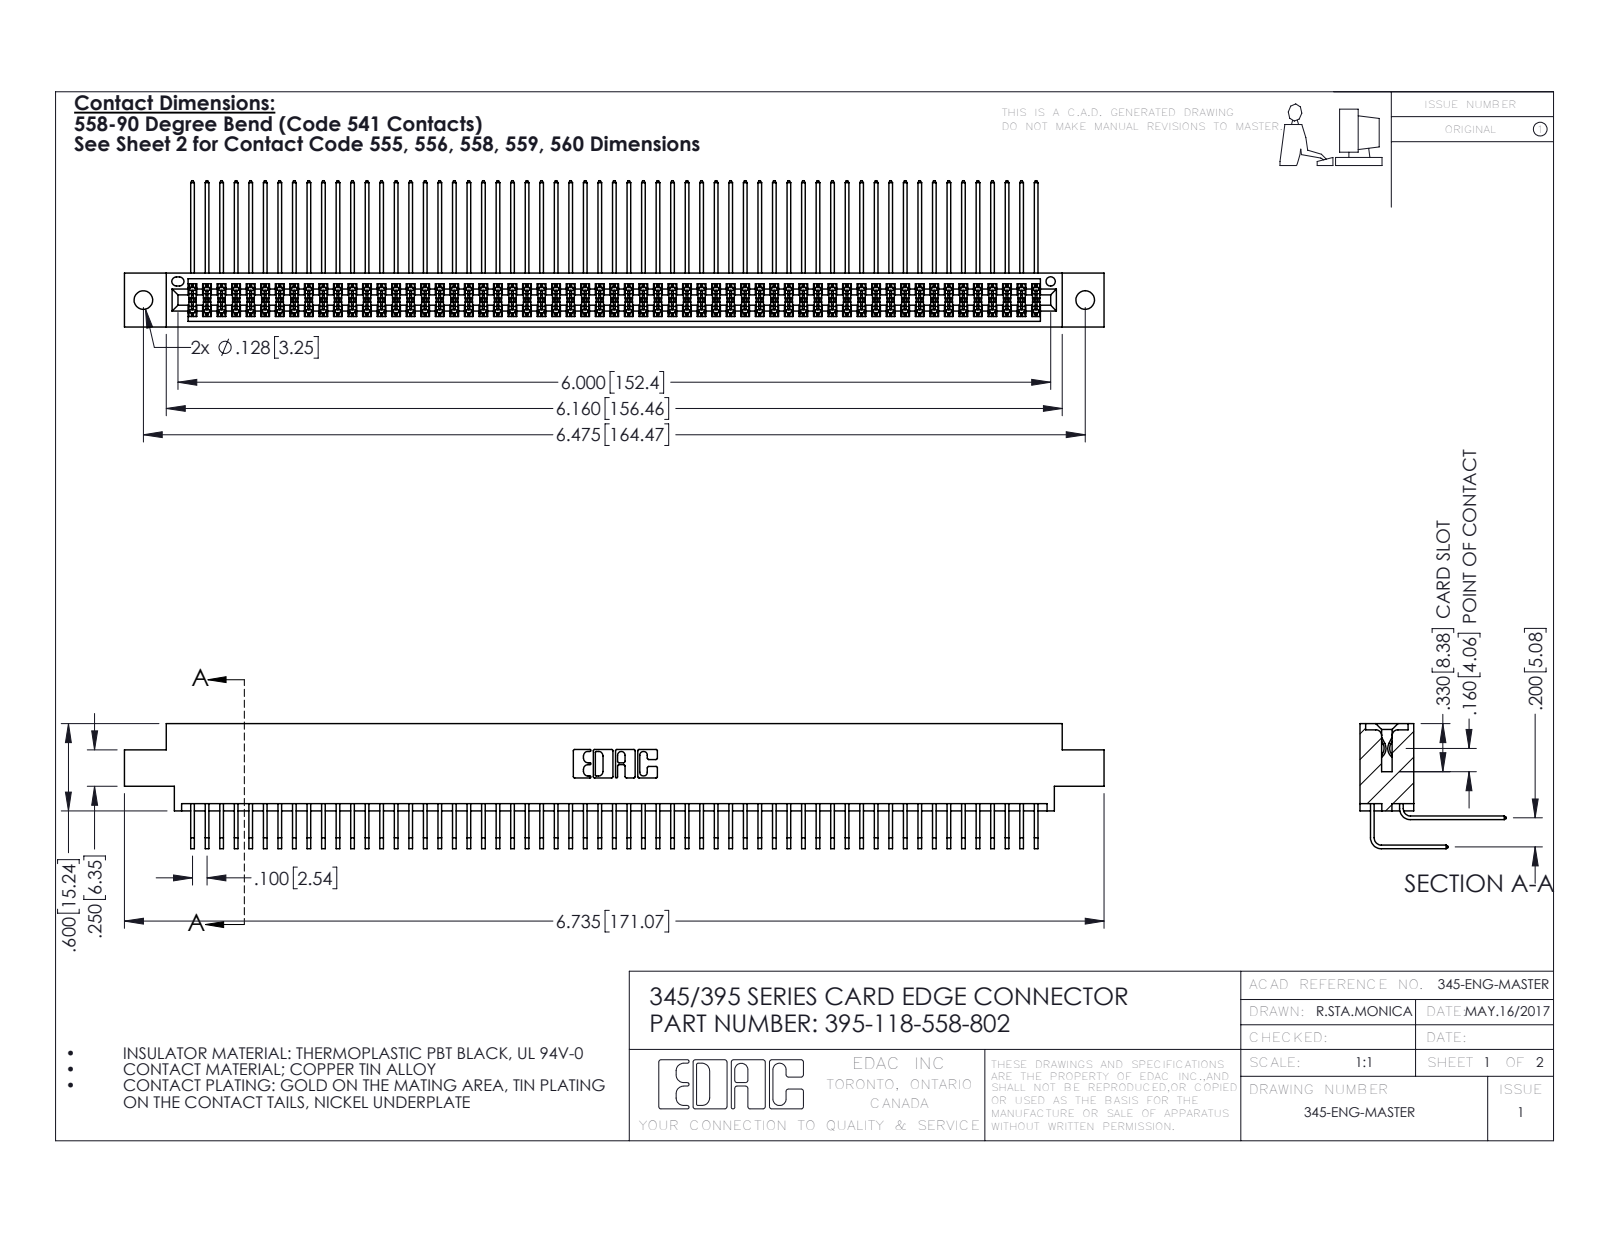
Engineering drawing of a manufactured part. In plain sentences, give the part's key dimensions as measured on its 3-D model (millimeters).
The part is named "395-118-558-802; 345 Part_0.170 Offset - 0.128 Dia; 345-292-001_558 559 Tail - 1; 345-292-001_558 Tail - 2". Its 3-D file was written by "SolidWorks 2016 (CONFIG_CONTROL_DESIGN)". It is 119 solids with 6266 faces: 4214 planar, 2052 cylindrical and 0 other. Overall it measures 171.1 by 25.5 by 21.8 millimeters. Its volume is 17 300 cubic millimeters and its surface area 28 980 square millimeters. Round holes: 2 of diameter 3.3, 1 of diameter 1.6. Partial cylindrical surfaces (rounded edges, fillets, slot ends): 178 of radius 0.2, 22 of radius 0.3, 6 of radius 0.2, 6 of radius 0.8, 3 of radius 0.7, 2 of radius 0.4, 2 of radius 0.5, 2 of radius 0.6. The main face-to-face distances are 1.8, 7.6, 5.1, 9.4, 2.5, 6.9, 0.6, 5.7, 4.4, 0.6. The hole center spacings are 6.9, 158.5, 164.5.
